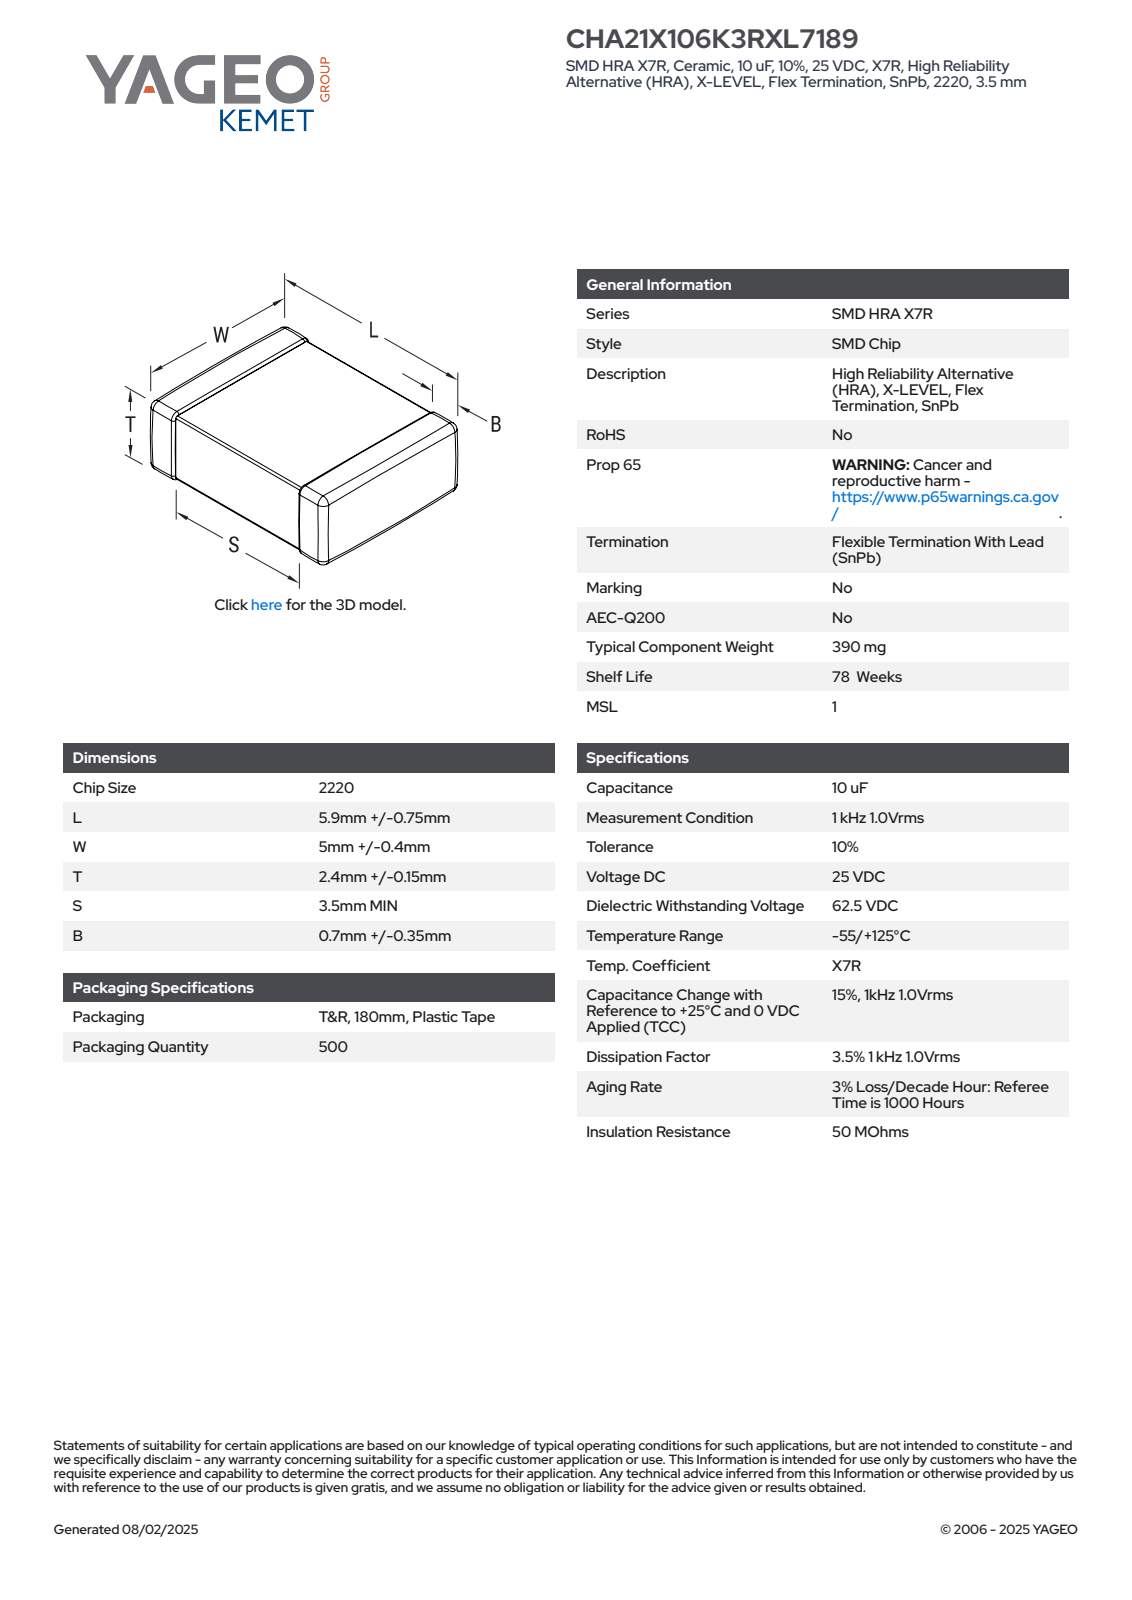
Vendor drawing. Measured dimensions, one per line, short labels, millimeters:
name: CCSM_STD_2220_L6.65W5.4T2.55S2.4B1.05
written by: SolidWorks 2021 (AUTOMOTIVE_DESIGN)
unit: mm
bodies: 4 solids, 121 faces (71 planar, 34 cylindrical, 16 other)
size: 6.65 × 5.4 × 2.55
volume: 83 mm³; area: 132 mm²
rounds: 24× R0.11
face distances: 2.33, 2.44, 6.65, 5.18, 2.55, 5.29, 5.4, 2.8, 3.85, 3.59
